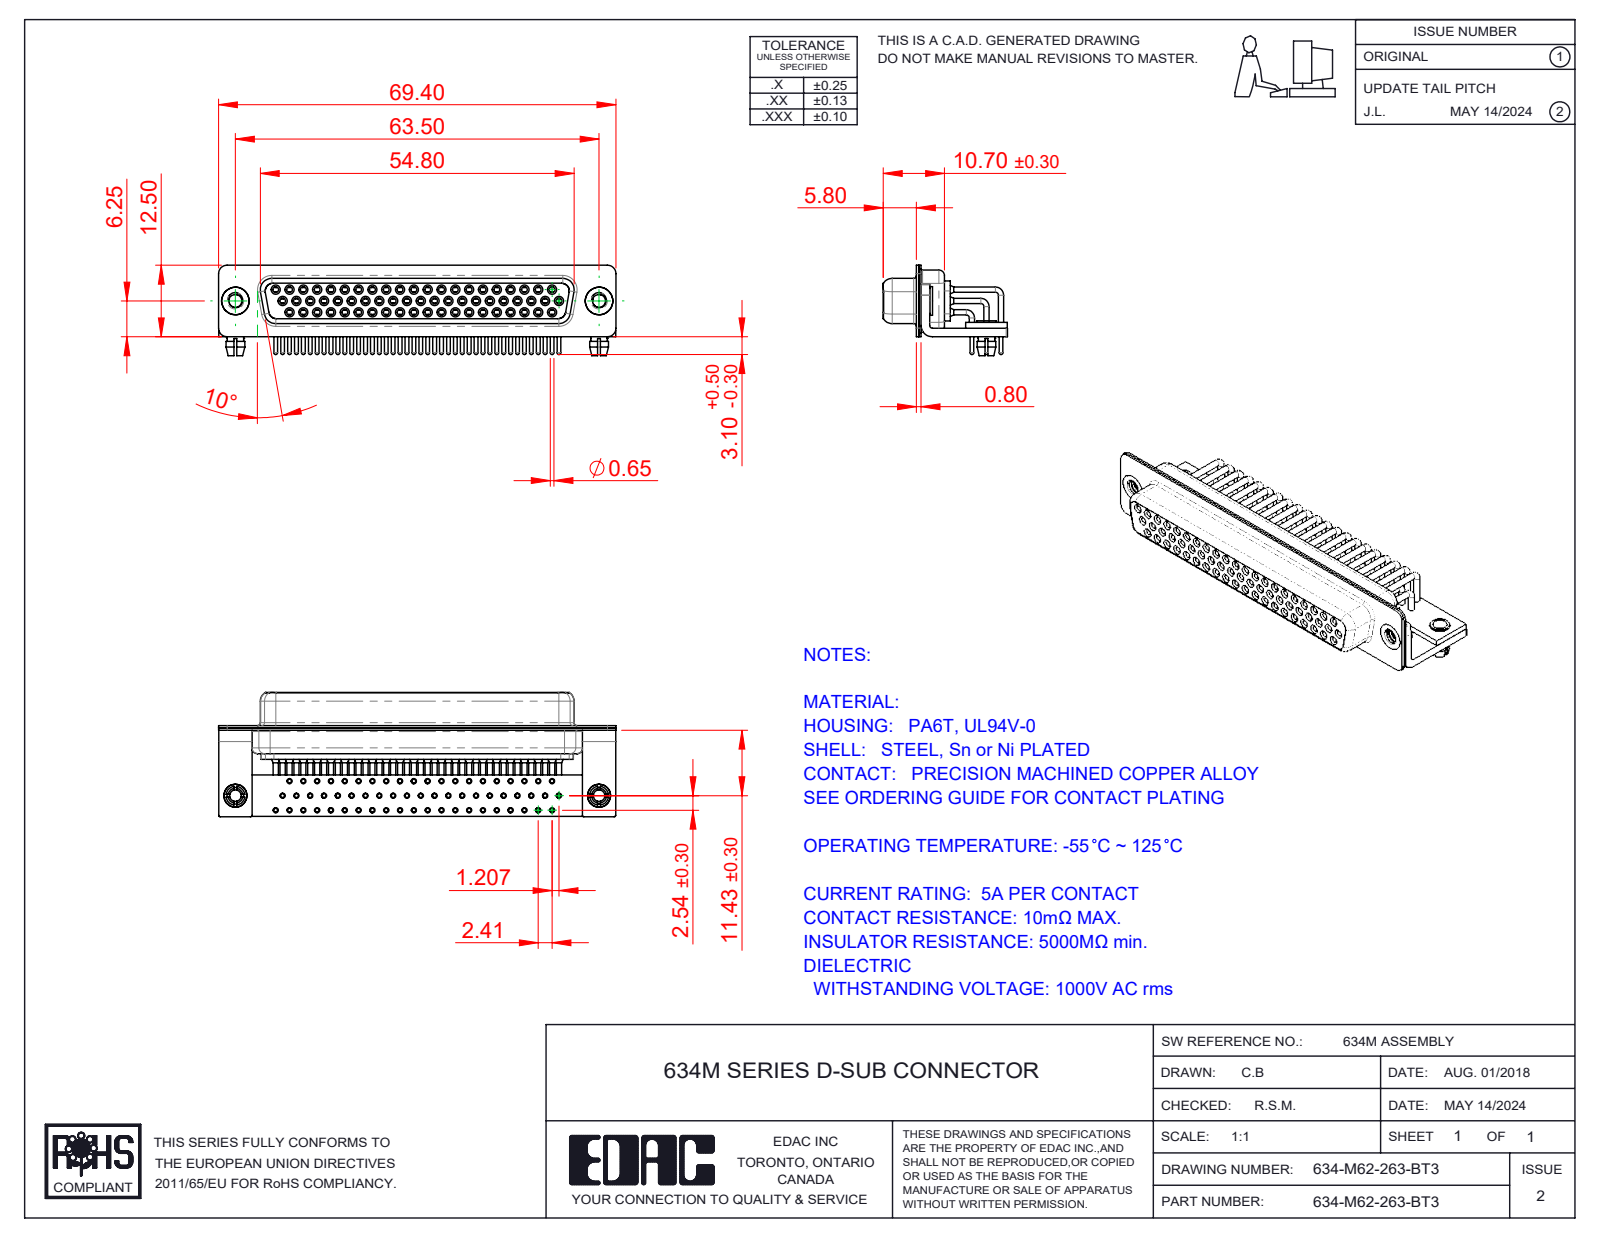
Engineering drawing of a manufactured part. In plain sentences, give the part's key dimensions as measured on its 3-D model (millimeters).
The part is named "634M Board Lock; 634M Shell Rear_62 Contacts; 634M Contact Row 3; 634M Housing_62 Contacts (+7 more)". Its 3-D file was written by "SolidWorks 2016 (CONFIG_CONTROL_DESIGN)". It is 72 solids with 3831 faces: 1071 planar, 1741 cylindrical and 1019 other. Overall it measures 69.4 by 21.7 by 15.8 millimeters. Its volume is 6 178 cubic millimeters and its surface area 19 963 square millimeters. Round holes: 64 of diameter 2, 62 of diameter 0.9, 62 of diameter 1, 62 of diameter 1.1, 62 of diameter 1.7, 62 of diameter 1.8, 2 of diameter 2.26, 2 of diameter 2.5, 2 of diameter 3.2, 2 of diameter 4, 2 of diameter 4.8. Round bosses or shafts: 118 of diameter 0.9, 62 of diameter 1.6, 62 of diameter 1.5, 62 of diameter 0.65, 56 of diameter 2, 2 of diameter 5, 2 of diameter 4.9, 2 of diameter 4. Partial cylindrical surfaces (rounded edges, fillets, slot ends): 16 of radius 0.25, 16 of radius 1.5, 13 of radius 2, 8 of radius 1.35, 8 of radius 1.6, 5 of radius 0.5, 4 of radius 0.6, 4 of radius 0.65. The main face-to-face distances are 0.4, 2.3, 1, 1.9, 1.45, 8.95, 8.5, 0.85, 0.8, 9.35. The hole center spacings are 7.24, 2.41, 9.65, 4.83, 14.48, 16.89, 2.81, 2.32.
